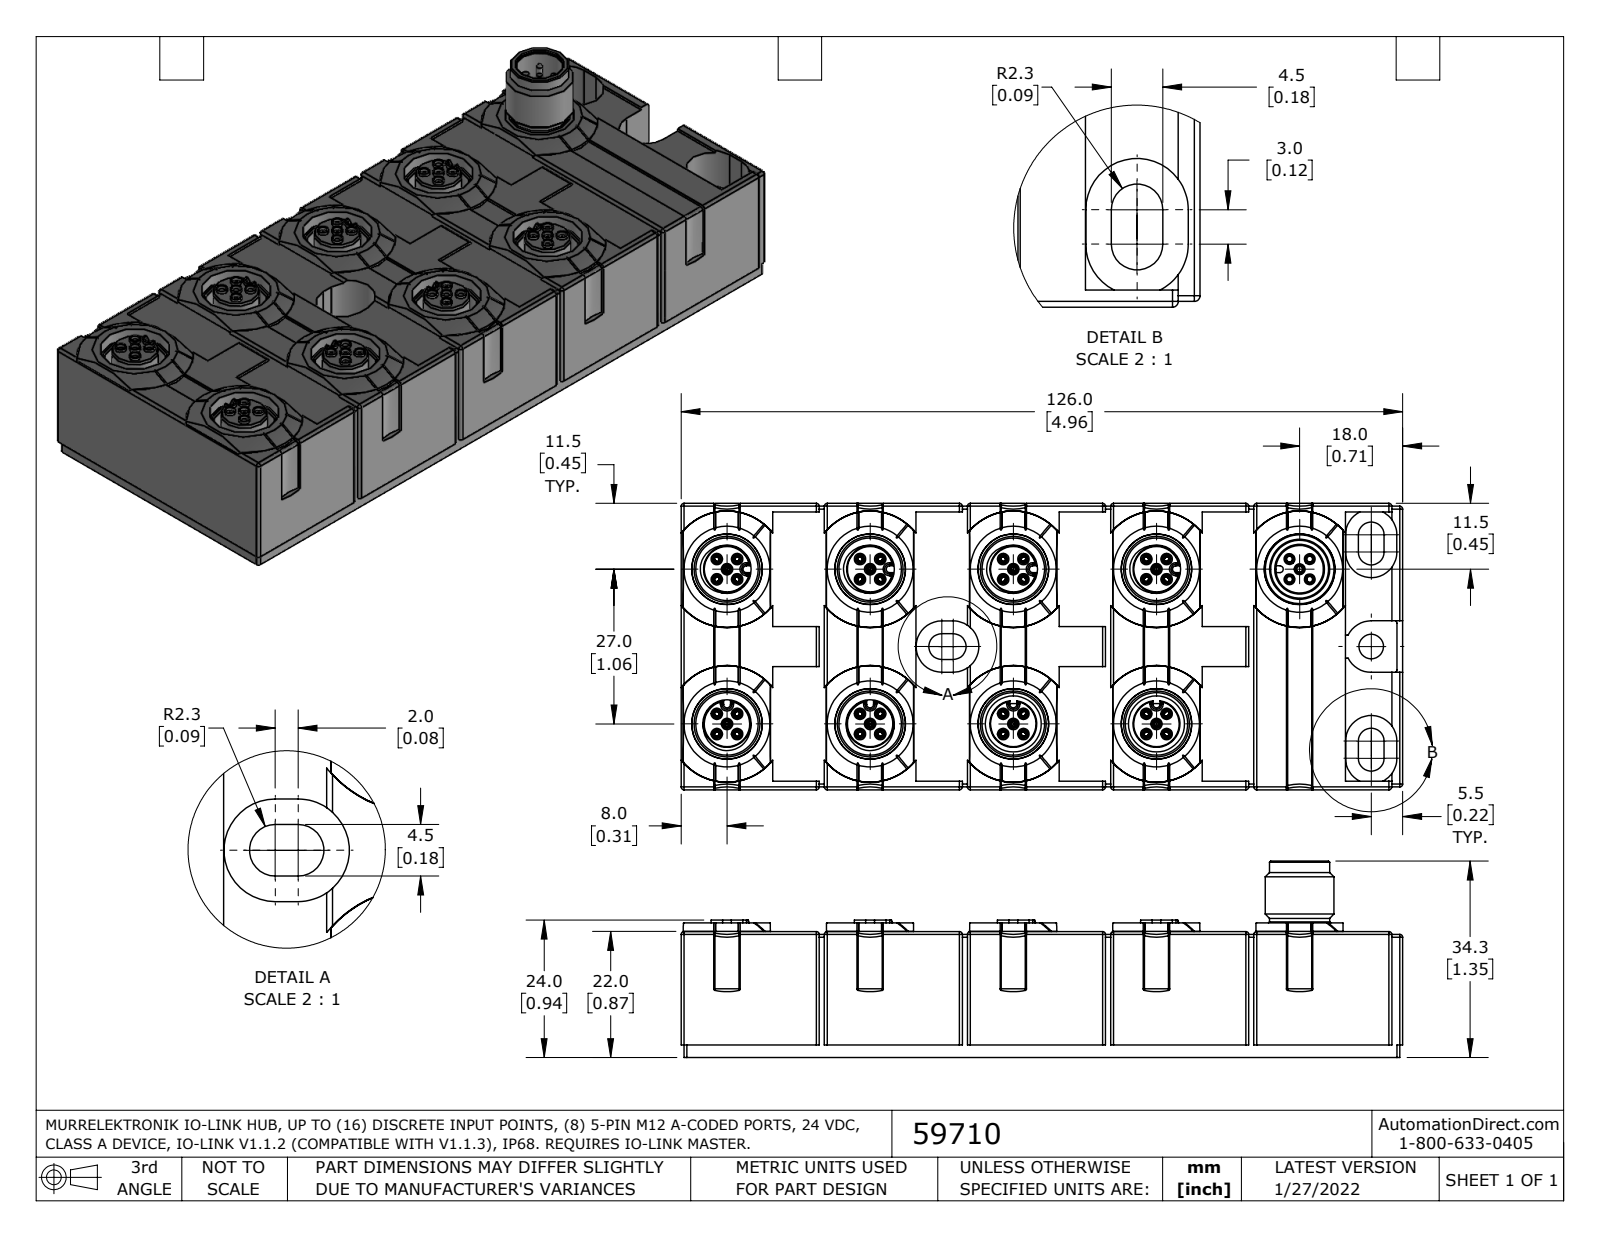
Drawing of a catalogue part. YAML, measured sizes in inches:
part_name: "59710"
step_written_by: "SolidWorks 2021 (AUTOMOTIVE_DESIGN)"
units: inches
bodies: {solids: 1, faces: 2573, planar: 630, cylindrical: 671, other: 1272}
overall_size: [4.961, 1.969, 1.35]
volume: 8.079
surface_area: 50.21
round_holes:
  - {diameter: 0.042, count: 40}
  - {diameter: 0.047, count: 40}
  - {diameter: 0.43, count: 6}
  - {diameter: 0.075, count: 5}
  - {diameter: 0.43, count: 2}
  - {diameter: 0.169, count: 1}
  - {diameter: 0.248, count: 1}
  - {diameter: 0.327, count: 1}
round_bosses_or_shafts:
  - {diameter: 0.079, count: 40}
  - {diameter: 0.059, count: 40}
  - {diameter: 0.323, count: 8}
  - {diameter: 0.049, count: 5}
  - {diameter: 0.039, count: 5}
  - {diameter: 0.484, count: 1}
  - {diameter: 0.472, count: 1}
  - {diameter: 0.413, count: 1}
partial_cylinders:
  - {radius: 0.02, count: 43}
  - {radius: 0.01, count: 30}
  - {radius: 0.394, count: 15}
  - {radius: 0.402, count: 9}
  - {radius: 0.024, count: 8}
  - {radius: 0.045, count: 8}
  - {radius: 0.089, count: 6}
  - {radius: 0.176, count: 6}
face_to_face_distances: [0.02, 1.969, 0.846, 0.866, 0.059, 0.079, 0.925, 4.961, 1.949, 0.276]
hole_center_spacings: [0.098, 0.139, 0.984, 0.917, 1.056, 0.994, 1.449, 0.197]
